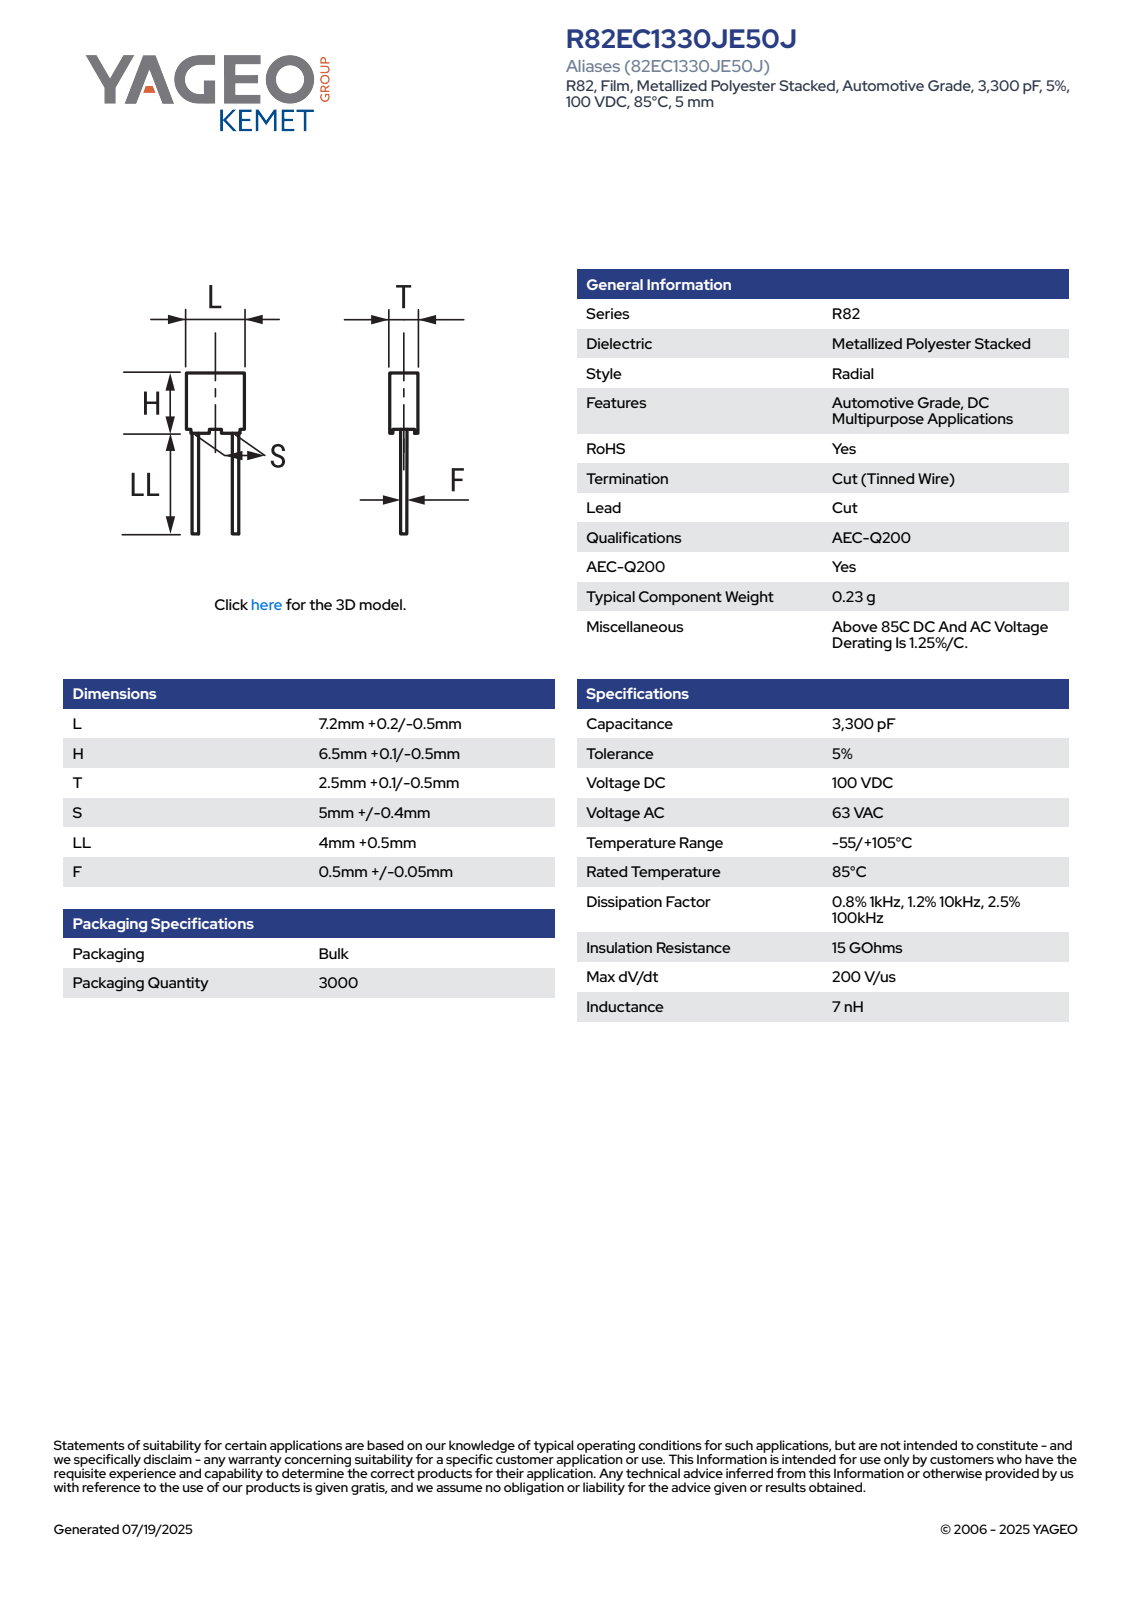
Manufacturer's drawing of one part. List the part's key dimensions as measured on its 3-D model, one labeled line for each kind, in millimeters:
Part name (STEP PRODUCT): CFR_RB3_7.2X6.5X2.5_L7.4H6.6T2.6S5LL4.5F0.55
STEP written by: SolidWorks 2014 (AUTOMOTIVE_DESIGN)
Units: millimetres
Bodies: 4 solids, 85 faces (77 planar, 8 cylindrical, 0 other)
Overall size (bounding box): 11.1 × 7.4 × 2.6
Volume: 117 mm³ · Surface area: 200 mm²
Round bosses / shafts (diameter × count): ⌀0.55 ×2
Partial cylindrical surfaces — rounded edges, fillets, slot ends (radius × count): R0.5 ×4
Main face-to-face distances: 2.6, 7.4, 5.85, 2.35, 2.1, 0.75, 6.6, 7.15, 6.9, 0.52
